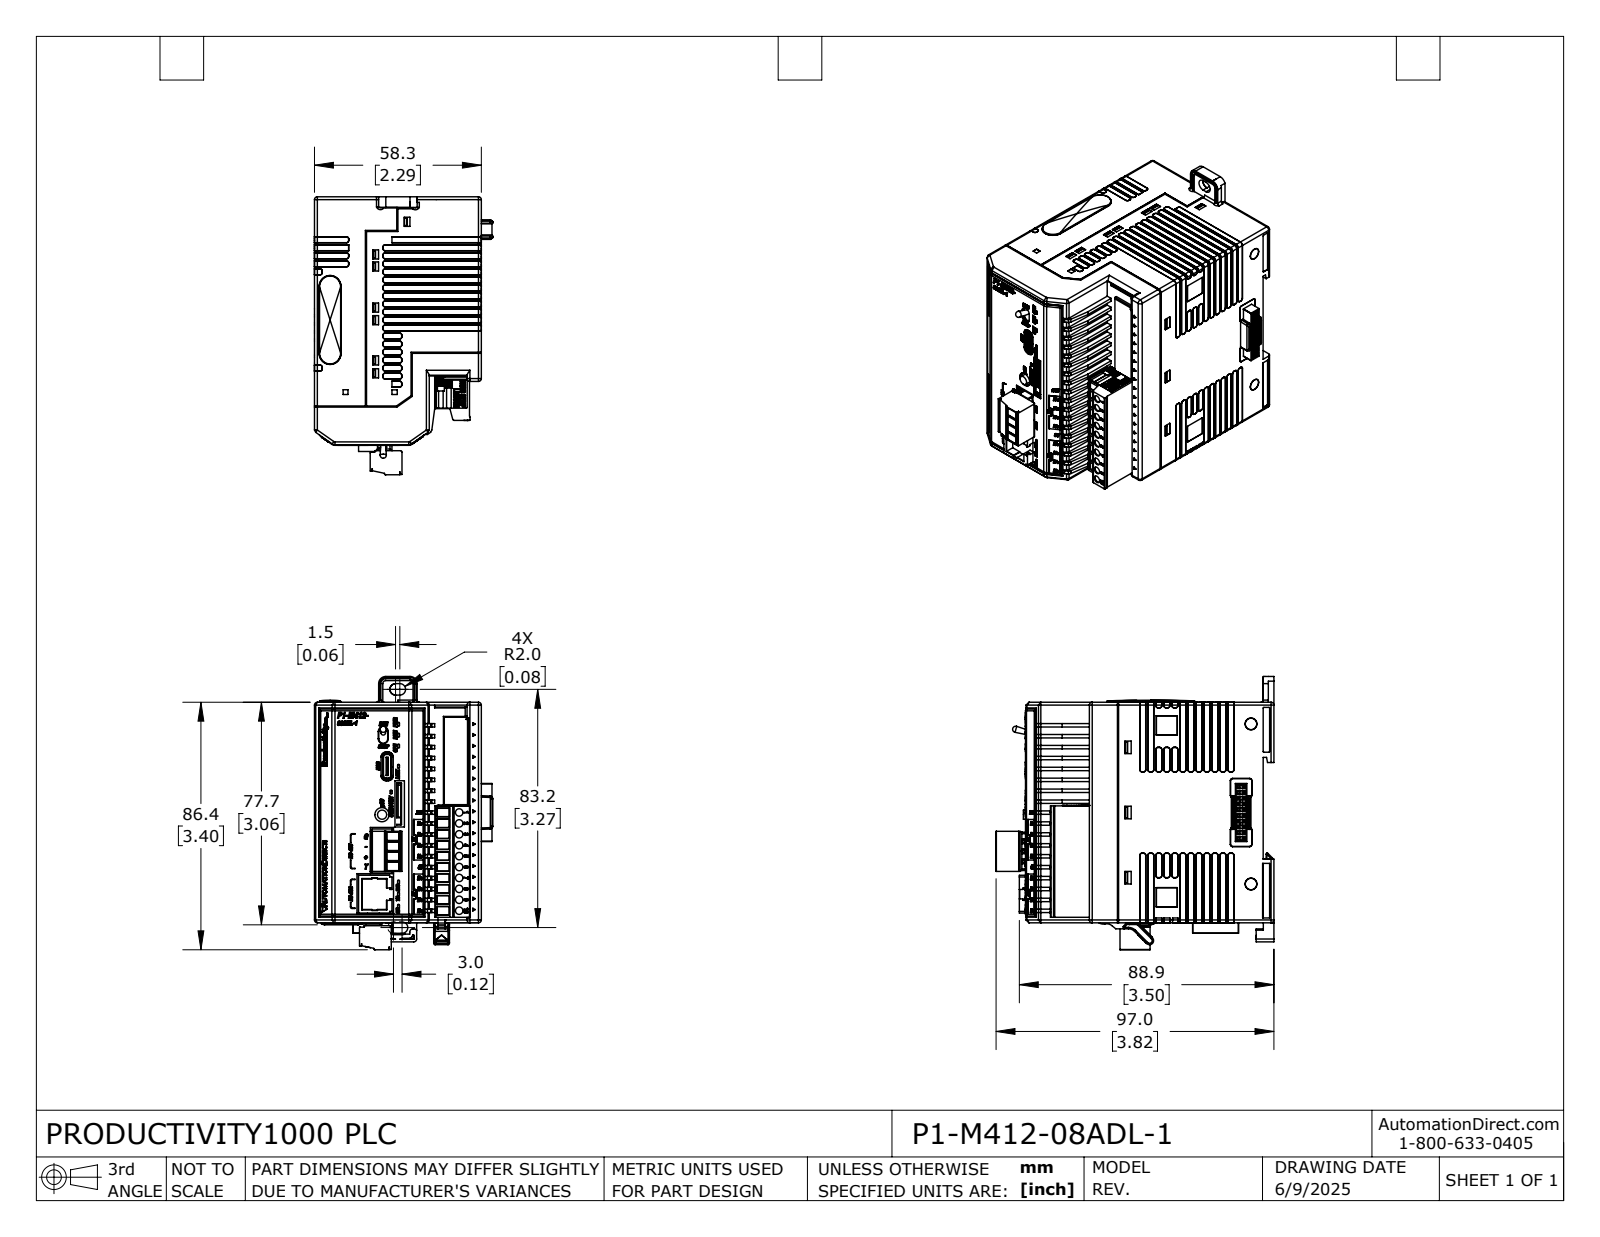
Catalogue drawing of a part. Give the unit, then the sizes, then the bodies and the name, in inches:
Units: inches
Overall size (bounding box): 3.686 × 3.593 × 2.452
Round holes (diameter × count): ⌀0.194 ×1
Round bosses / shafts (diameter × count): ⌀0.214 ×1, ⌀0.126 ×1
Partial cylindrical surfaces — rounded edges, fillets, slot ends (radius × count): R0.01 ×172, R0.008 ×86, R0.02 ×49, R0.039 ×33, R0.079 ×8, R0.024 ×7, R0.004 ×6, R0.012 ×4
Main face-to-face distances: 2.235, 0.02, 0.039, 2.275, 3.01, 3.022, 2.294, 2.294, 2.255, 3.02
Volume: 2.127 in³ · Surface area: 106.4 in²
Bodies: 27 solids, 3723 faces (2139 planar, 899 cylindrical, 685 other)
Part name (STEP PRODUCT): P1-M412-08ADL-1
STEP written by: SolidWorks 2024 (AUTOMOTIVE_DESIGN)
